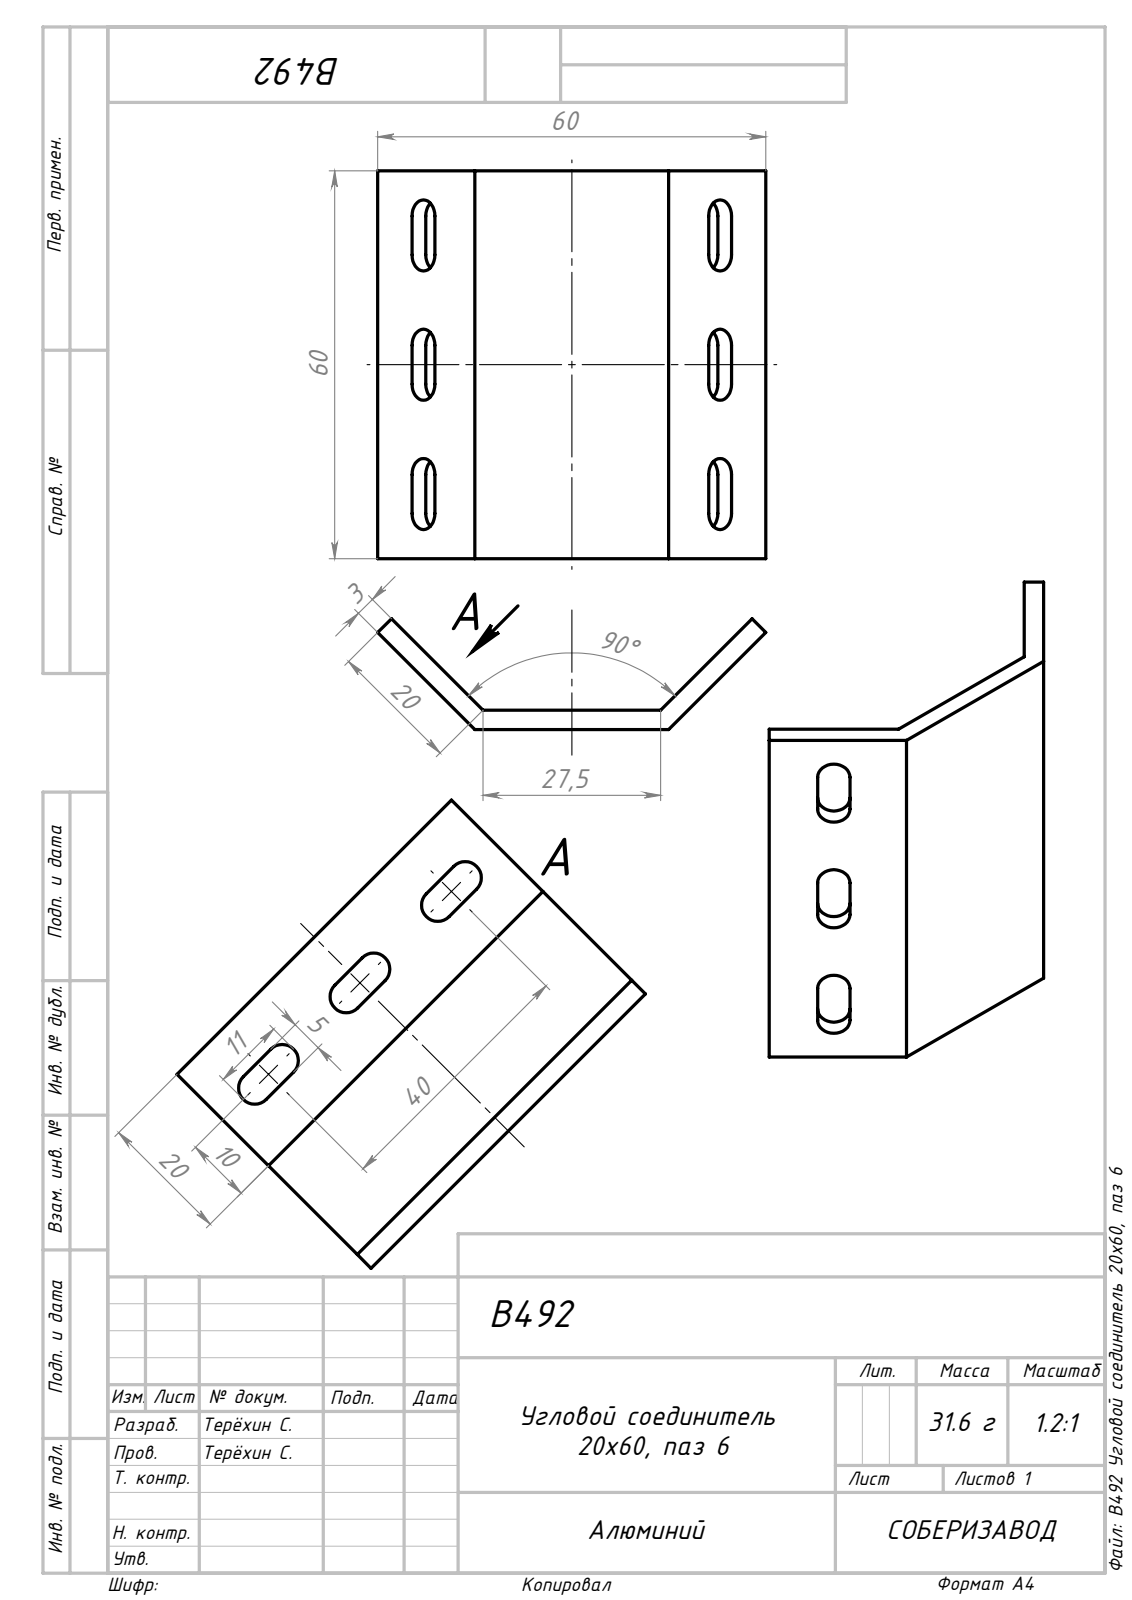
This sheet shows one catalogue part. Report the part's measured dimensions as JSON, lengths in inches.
{"part_name": "Сборка5; B492 Угловой соединитель 20x60, паз 6_00", "step_written_by": "SolidWorks 2022 (AUTOMOTIVE_DESIGN)", "units": "inches", "bodies": {"solids": 1, "faces": 34, "planar": 22, "cylindrical": 12, "other": 0}, "overall_size": [2.362, 2.362, 0.675], "volume_in3": 0.714, "surface_area_in2": 14.07, "partial_cylinders_radius": [[0.098, 12]], "face_to_face_distances": [0.118, 1.552, 1.67, 2.362, 0.492, 1.06, 1.178, 0.295, 0.197, 1.257]}
